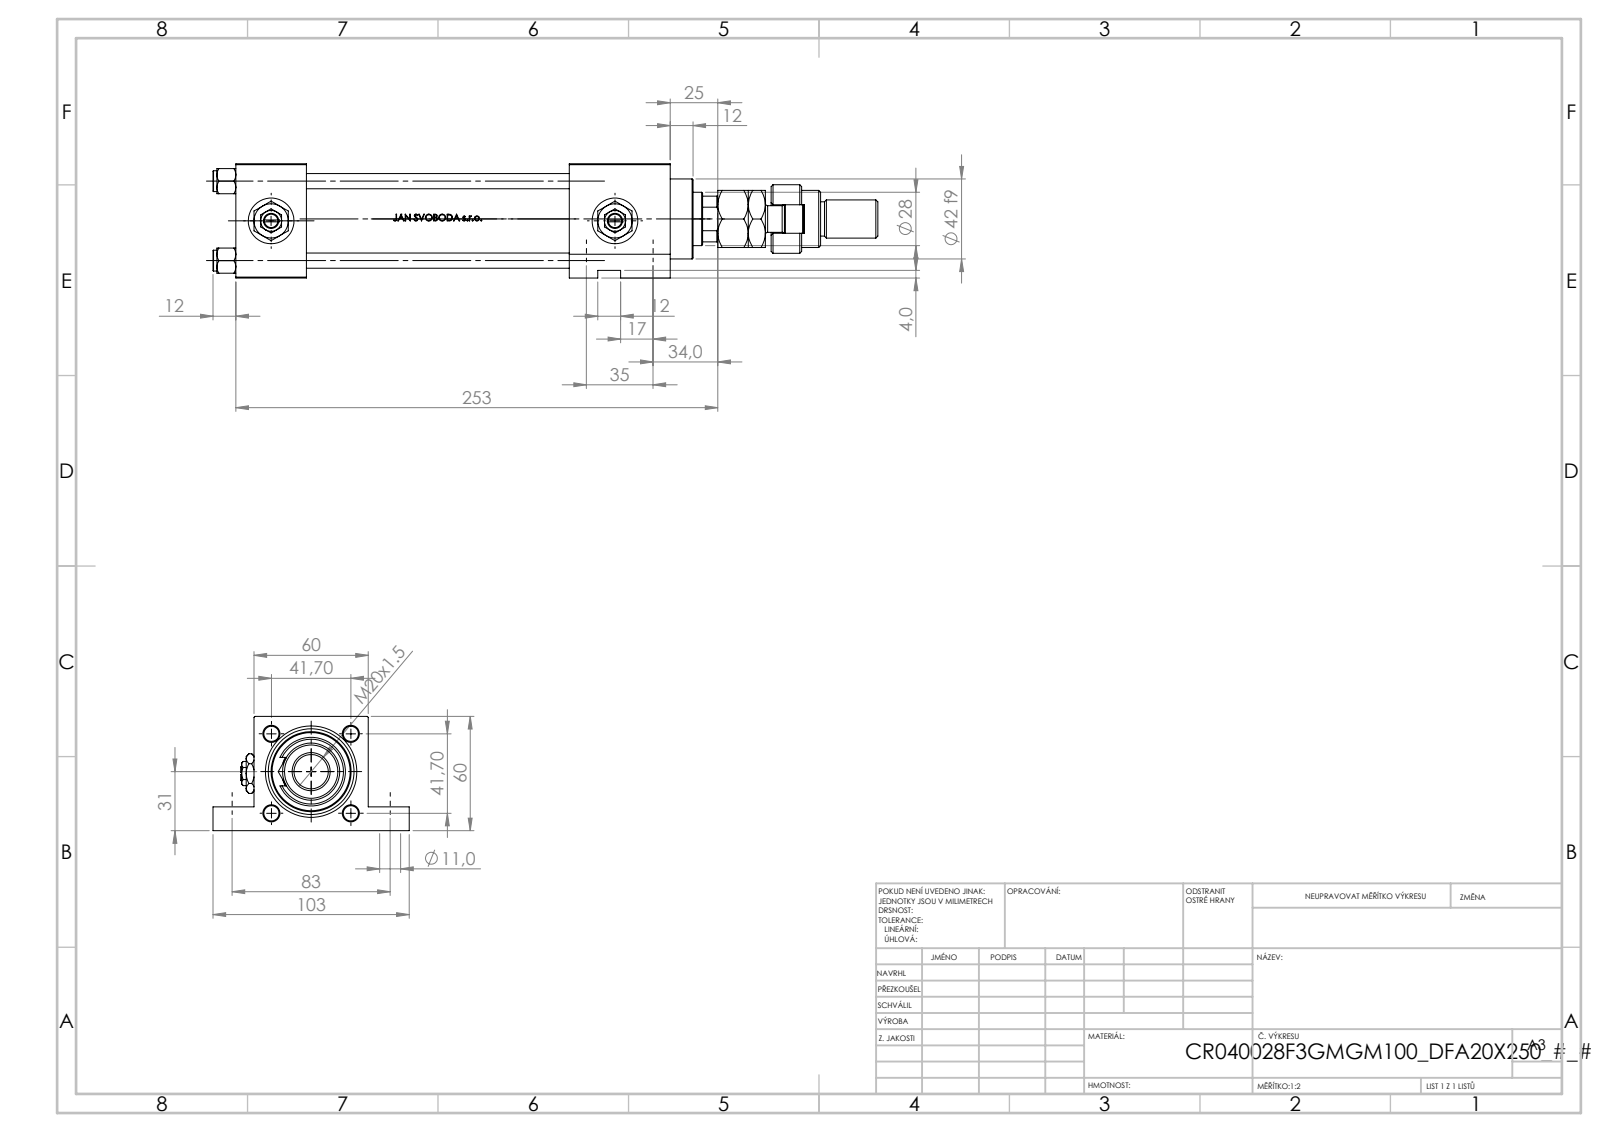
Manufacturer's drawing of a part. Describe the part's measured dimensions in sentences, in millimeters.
The part is named "V215CR_F_TYCINKA; V215CR_VCP_F; NUT_M5_F; V215CR_F_Body (+4 more)". Its 3-D file was written by "SolidWorks 2019 (CONFIG_CONTROL_DESIGN)". It is 15 solids with 1300 faces: 512 planar, 162 cylindrical and 626 other. Overall it measures 349 by 103 by 60 millimeters. Its volume is 588 447 cubic millimeters and its surface area 170 561 square millimeters. Round holes: 4 of diameter 8, 4 of diameter 11, 3 of diameter 16.66, 3 of diameter 24, 2 of diameter 7, 1 of diameter 16, 1 of diameter 18.5, 1 of diameter 28, 1 of diameter 31, 1 of diameter 40, 1 of diameter 45. Round bosses or shafts: 4 of diameter 11, 1 of diameter 46, 1 of diameter 42, 1 of diameter 36, 1 of diameter 30, 1 of diameter 22, 1 of diameter 20, 1 of diameter 18. Partial cylindrical surfaces (rounded edges, fillets, slot ends): 1 of radius 7.5, 1 of radius 12, 1 of radius 13.5. The main face-to-face distances are 60, 37, 53, 175, 138, 228, 38, 191, 12.5, 47.5. The hole center spacings are 41.7, 28.79, 30.2, 35, 58.97, 83, 90.08, 8.
